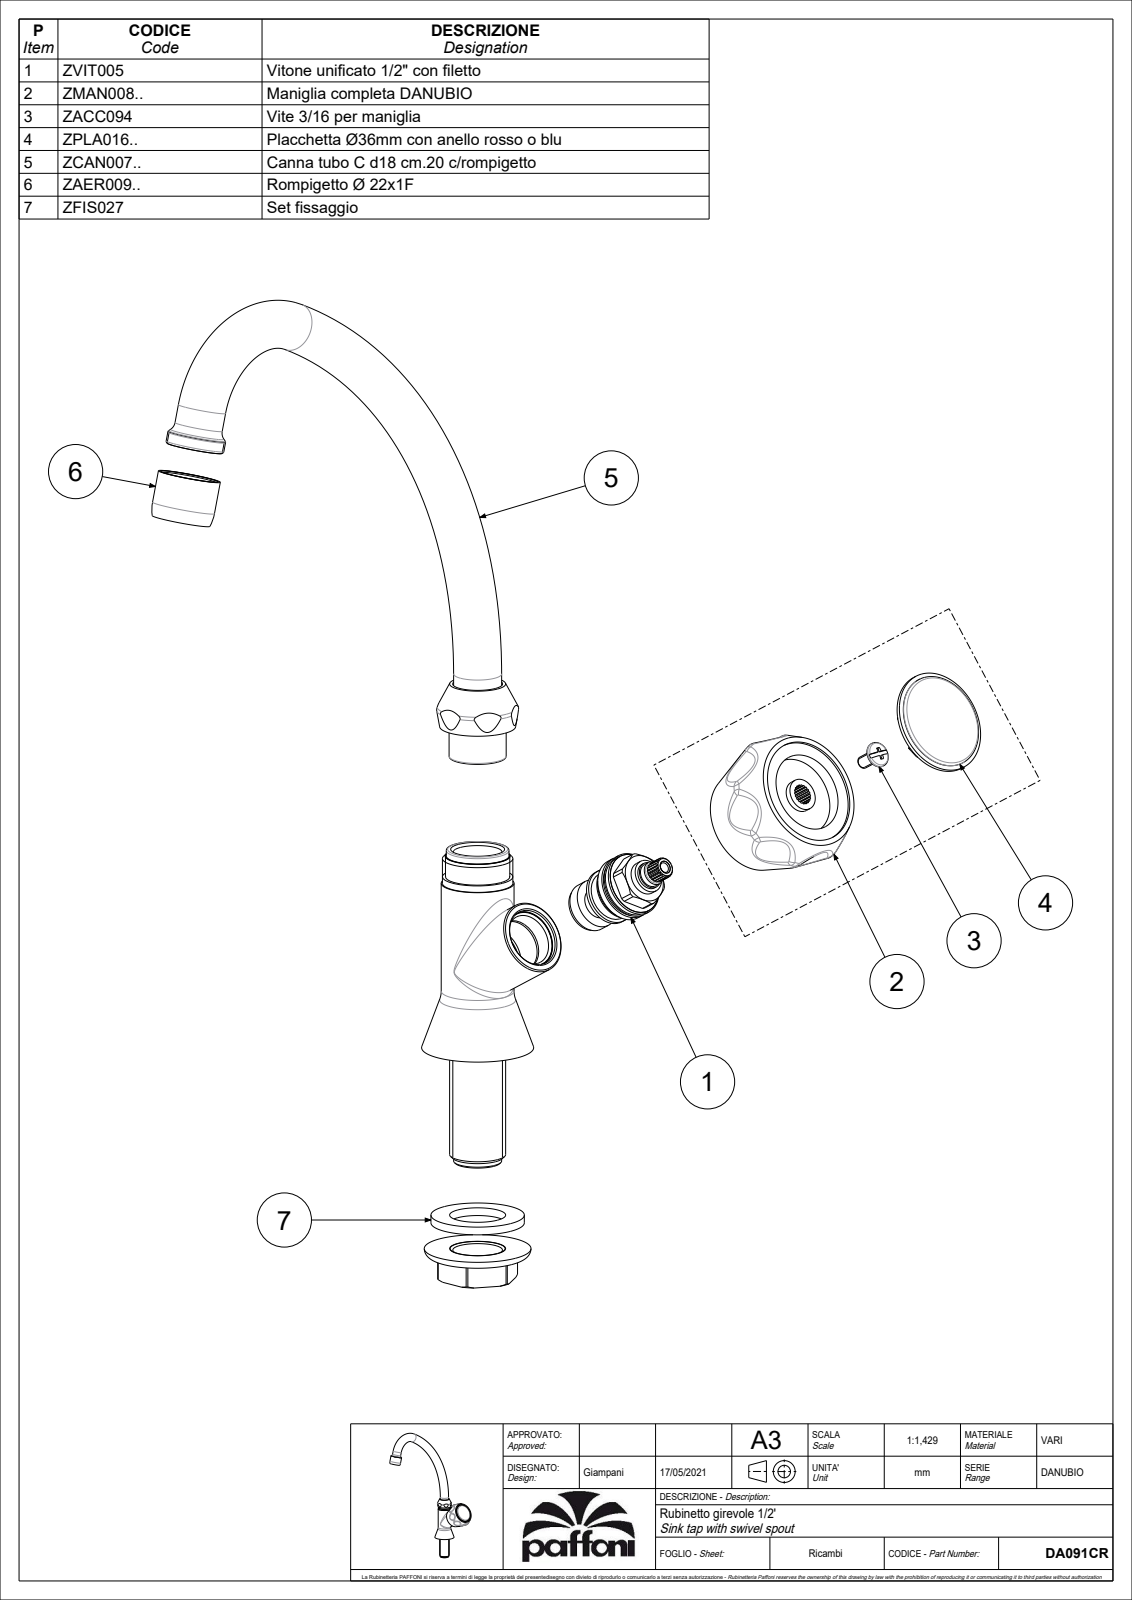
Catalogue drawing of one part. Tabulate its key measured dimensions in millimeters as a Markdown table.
| quantity | value |
| --- | --- |
| part name | DA091CR |
| STEP written by | CREO PARAMETRIC BY PTC INC, 2020044 (CONFIG_CONTROL_DESIGN) |
| units | millimeters |
| bodies | 1 solid, 125 faces (15 planar, 24 cylindrical, 86 other) |
| overall size | 255.5 × 188.6 × 90.29 |
| volume | 204 921 mm³ |
| surface area | 35 522 mm² |
| round holes (diameter × count) | 26.9 × 1 |
| round bosses / shafts (diameter × count) | 18 × 2, 38.5 × 1, 27.3 × 1, 27.2 × 1, 26.4 × 1, 23.6 × 1 |
| partial cylindrical surfaces (radius × count) | 21.31 × 8 |
| main face-to-face distances | 35.3, 35.7, 0.4, 29, 86.2, 69.7, 16.5, 17, 63.8, 5.9 |
